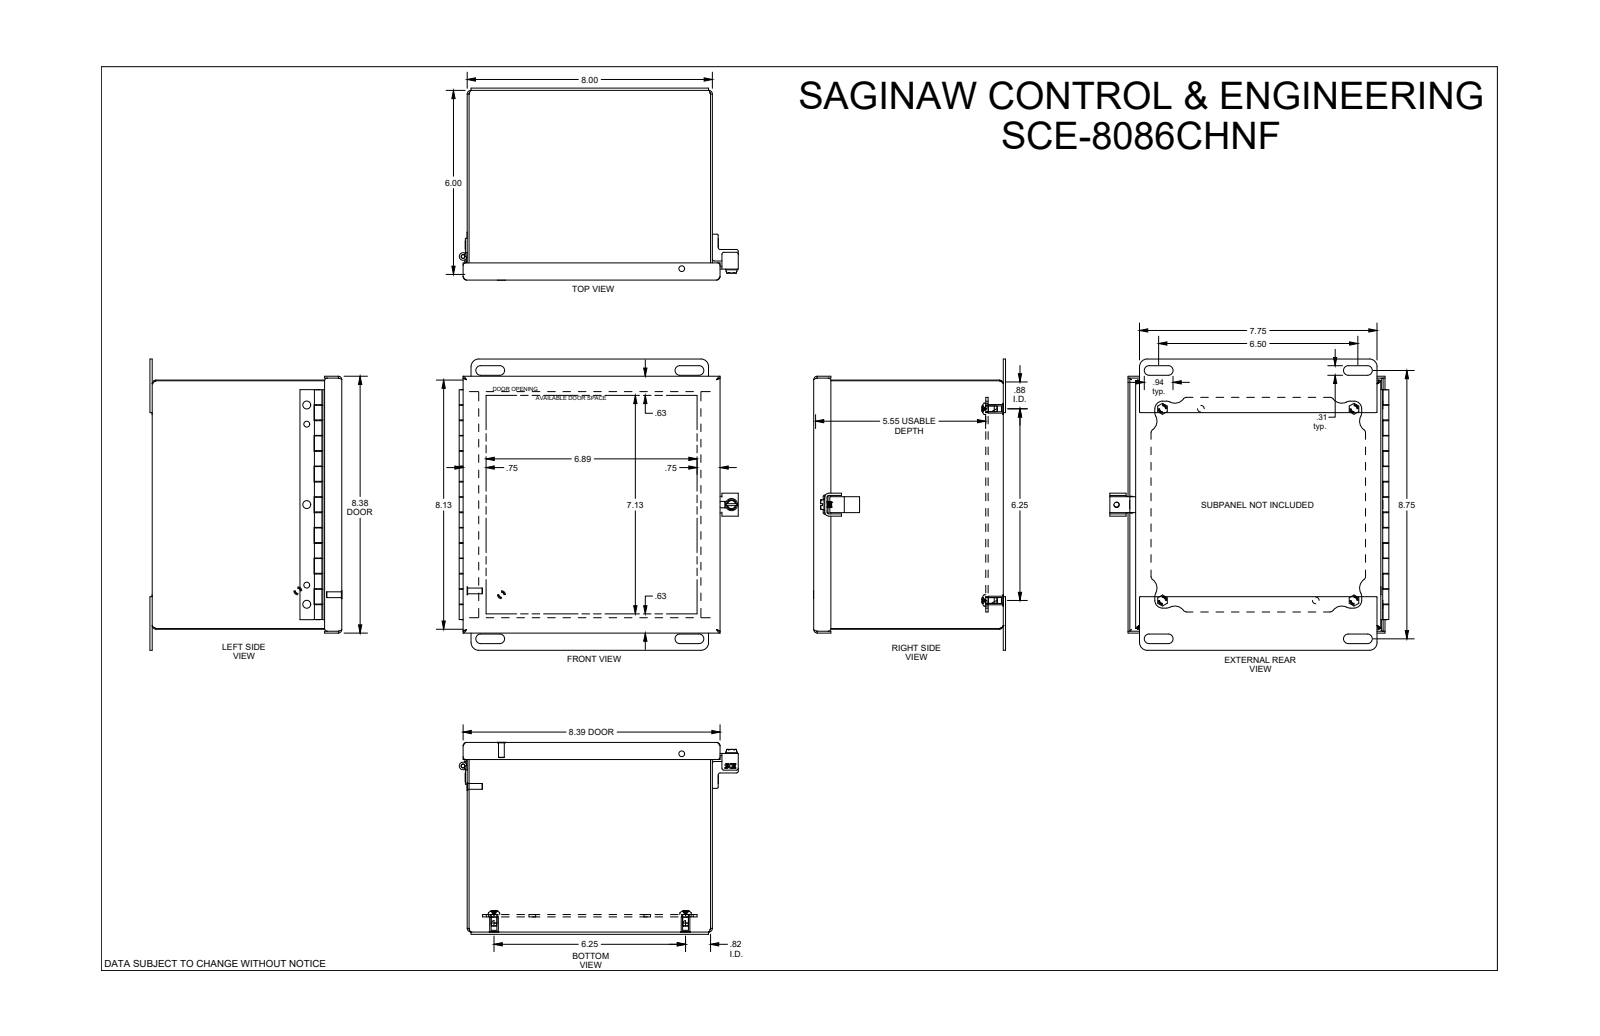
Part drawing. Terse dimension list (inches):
name: SCE-8086CHNF
written by: SolidWorks 2019 (CONFIG_CONTROL_DESIGN)
unit: in
bodies: 0 solids, 1091 faces (500 planar, 293 cylindrical, 298 other)
size: 9.5 × 9.104 × 6.265
holes: 8× ⌀0.19, 6× ⌀0.193, 4× ⌀0.25, 4× ⌀0.281, 2× ⌀0.193, 2× ⌀0.218, 1× ⌀0.126, 1× ⌀0.156, 1× ⌀0.187, 1× ⌀0.266
bosses: 11× ⌀0.188, 6× ⌀0.256, 4× ⌀0.373, 4× ⌀0.28, 1× ⌀0.396, 1× ⌀0.246, 1× ⌀0.123
rounds: 56× R0.01, 16× R0.25, 13× R0.06, 8× R0.052, 8× R0.112, 8× R0.125, 8× R0.156, 8× R0.344
face distances: 0.06, 0.06, 7.94, 6.125, 6.185, 6.065, 6.125, 0.075, 8, 5.63
hole spacings: 6.25, 1.25, 3.25, 3.251, 5, 6.374, 8.004, 8.356
